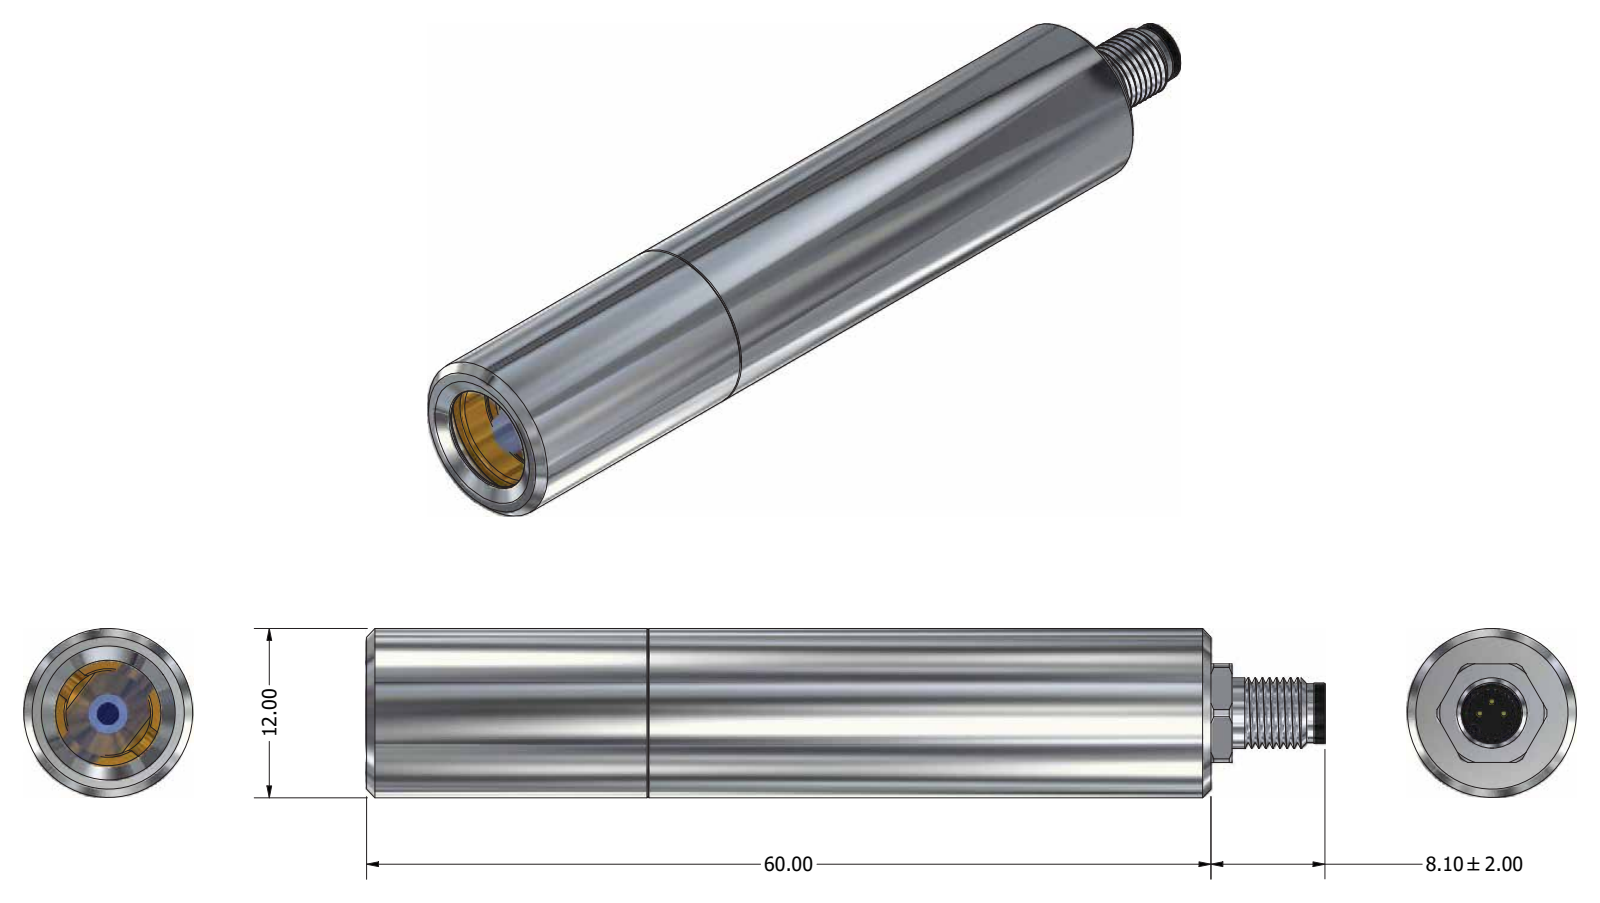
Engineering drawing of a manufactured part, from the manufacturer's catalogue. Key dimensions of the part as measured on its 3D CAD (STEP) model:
Part name (STEP PRODUCT): lwpro12; front; back; m5-3p_realthread
STEP written by: unknown (AUTOMOTIVE_DESIGN)
Units: millimetres
Bodies: 4 solids, 109 faces (24 planar, 40 cylindrical, 45 other)
Overall size (bounding box): 68.1 × 12 × 12
Volume: 2 423 mm³ · Surface area: 4 891 mm²
Round holes (diameter × count): ⌀3.5 ×1, ⌀4.26 ×1, ⌀4.46 ×1, ⌀7.5 ×1, ⌀10 ×1, ⌀10.65 ×1, ⌀10.75 ×1
Round bosses / shafts (diameter × count): ⌀1 ×3, ⌀0.4 ×3, ⌀12 ×1, ⌀5 ×1, ⌀4.3 ×1, ⌀4.2 ×1
Partial cylindrical surfaces — rounded edges, fillets, slot ends (radius × count): R0.5 ×1, R3.9 ×1
Main face-to-face distances: 40, 59.25, 19.25, 1.5, 41.5, 60.75, 61.5, 60, 20, 0.75
